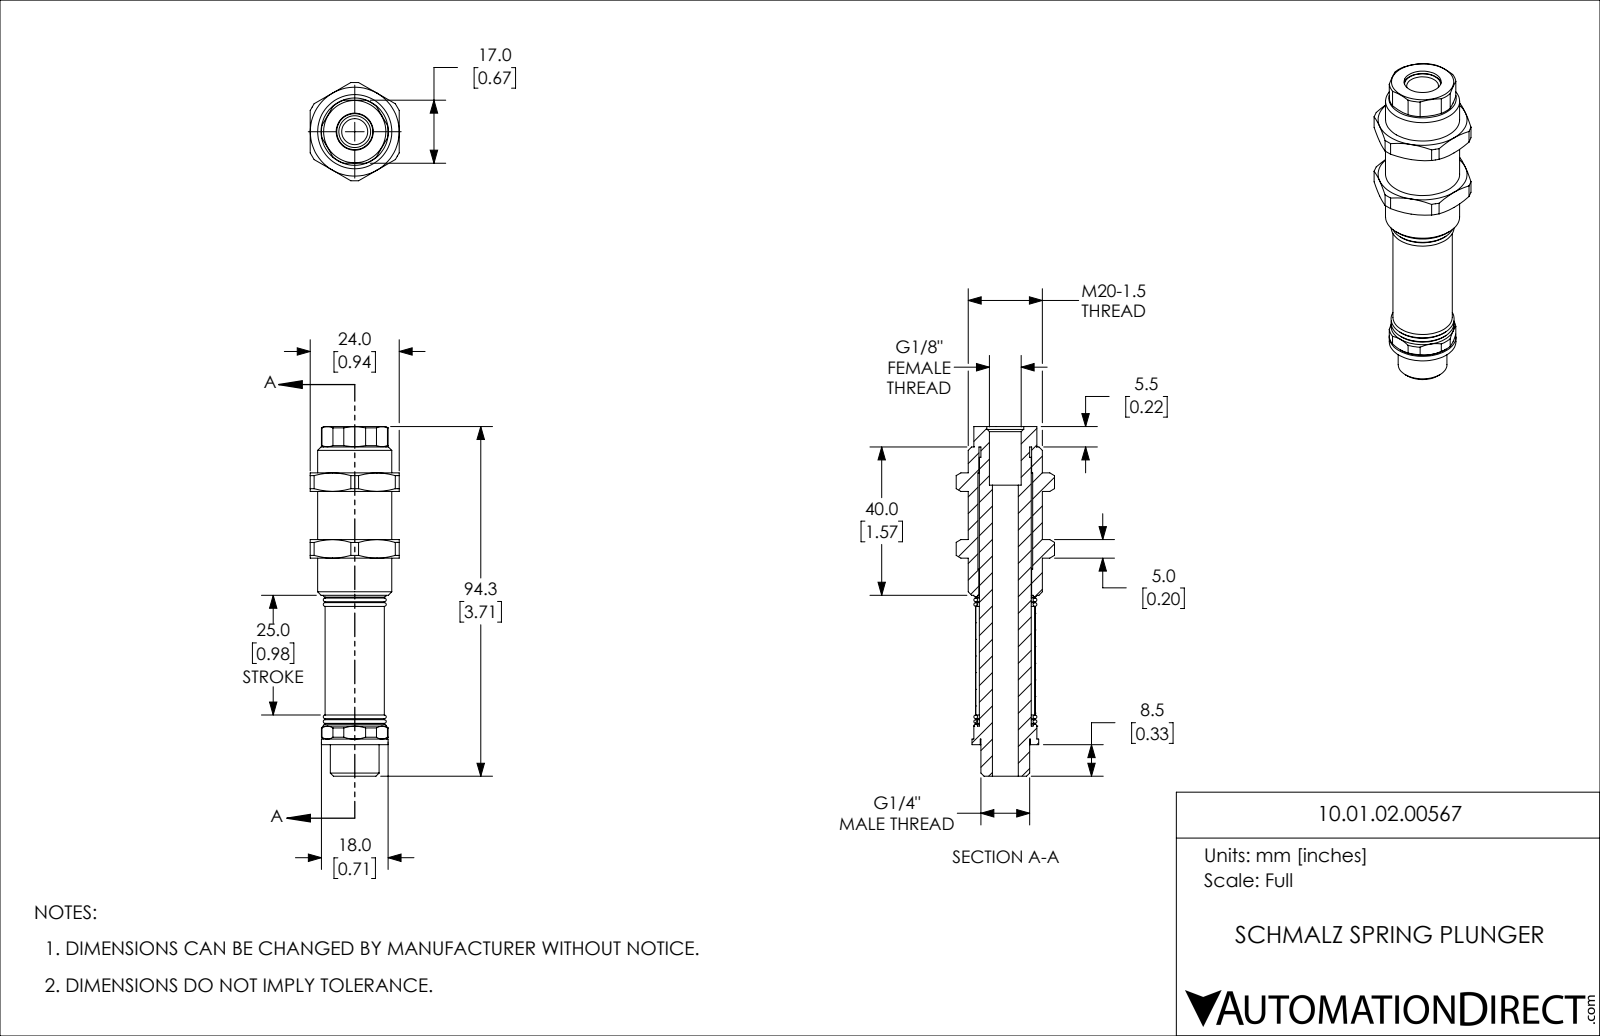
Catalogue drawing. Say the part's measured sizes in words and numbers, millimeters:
The part is named "10.01.02.00567". Its 3-D file was written by "SolidWorks 2021 (CONFIG_CONTROL_DESIGN)". It is 1 solid with 200 faces: 56 planar, 60 cylindrical and 84 other. Overall it measures 94.3 by 26.51 by 24 millimeters. Its volume is 19 056 cubic millimeters and its surface area 16 184 square millimeters. Round holes: 1 of diameter 7, 1 of diameter 8.57, 1 of diameter 10, 1 of diameter 13.5, 1 of diameter 14.2, 1 of diameter 14.8, 1 of diameter 16. Round bosses or shafts: 1 of diameter 20, 1 of diameter 18, 1 of diameter 16, 1 of diameter 14, 1 of diameter 13.16. The main face-to-face distances are 24, 5, 18, 17, 12.5, 30.5, 13, 17.5, 23, 35.5.
